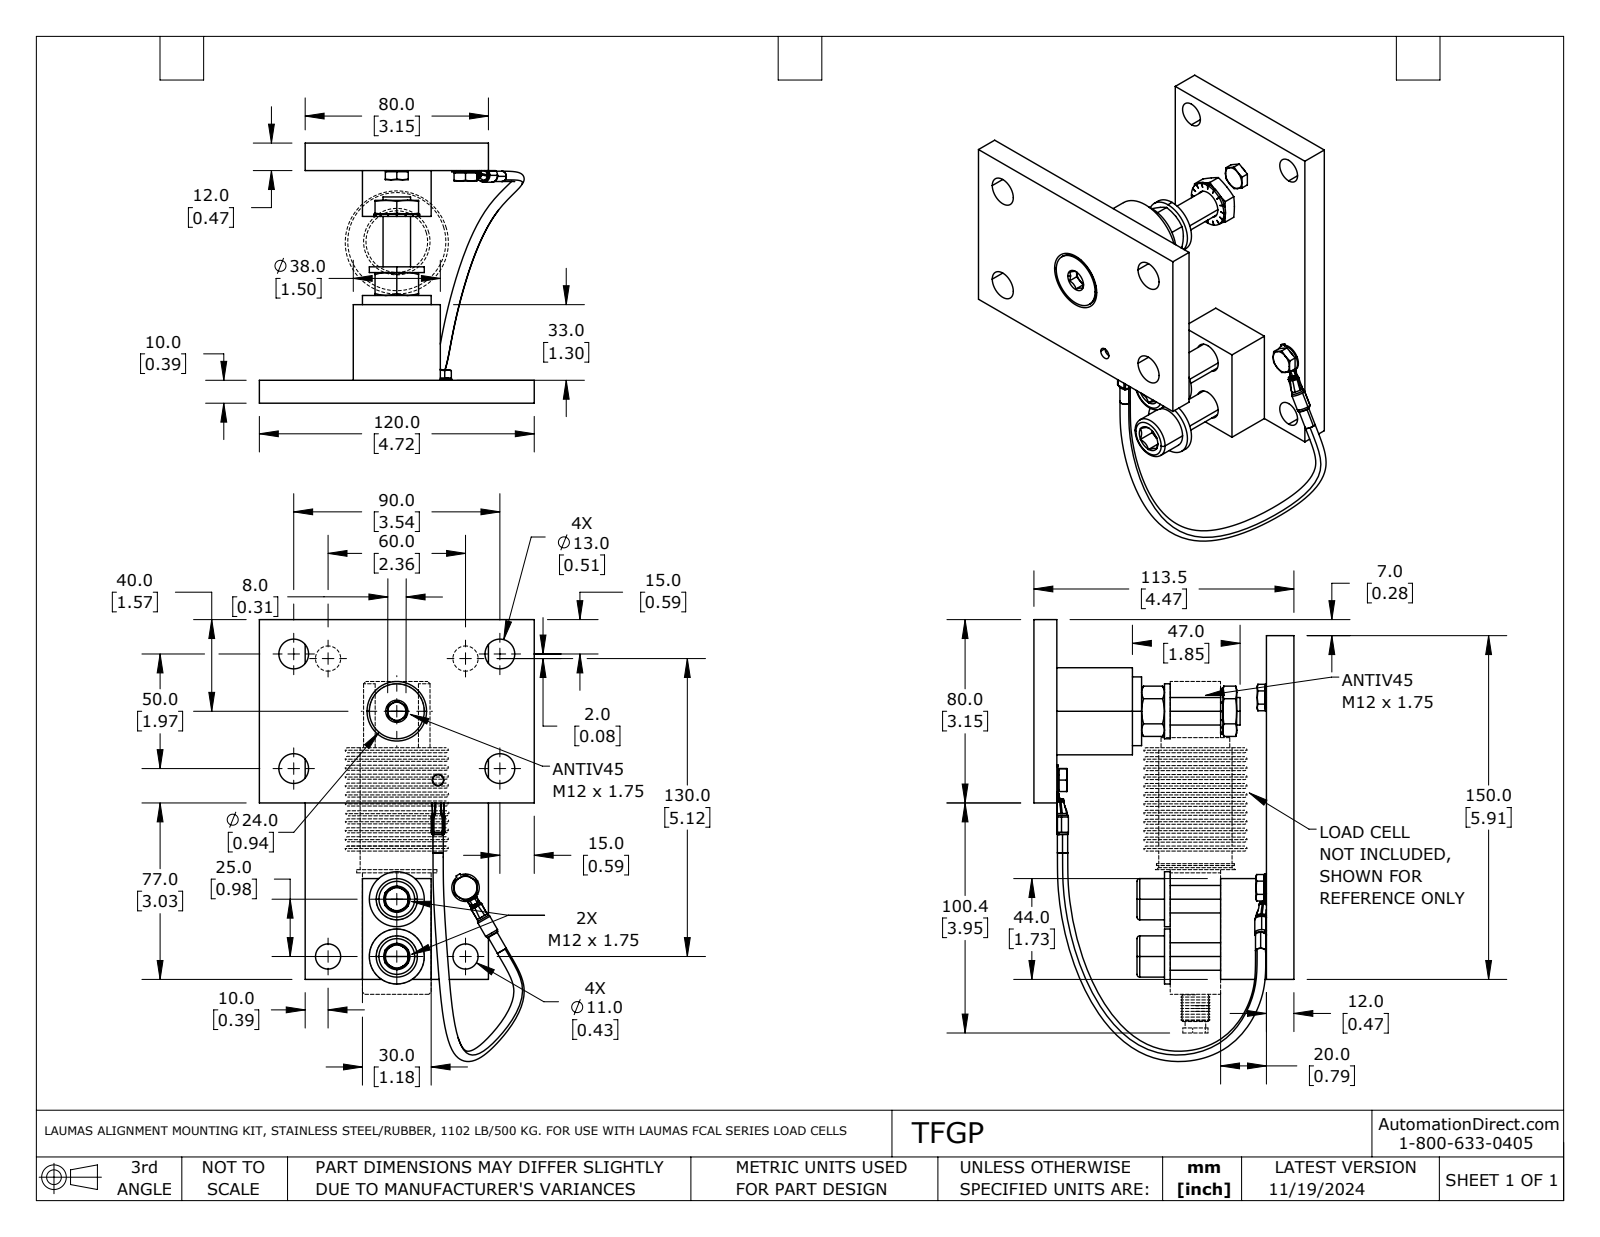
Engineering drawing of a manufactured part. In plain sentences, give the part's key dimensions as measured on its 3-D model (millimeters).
The part is named "TFGP". Its 3-D file was written by "SolidWorks 2021 (AUTOMOTIVE_DESIGN)". It is 24 solids with 639 faces: 230 planar, 190 cylindrical and 219 other. Overall it measures 192.8 by 120 by 113.5 millimeters. Its volume is 315 100 cubic millimeters and its surface area 103 400 square millimeters. Round holes: 7 of diameter 13, 4 of diameter 11, 3 of diameter 5, 3 of diameter 10.2, 2 of diameter 4, 2 of diameter 6, 1 of diameter 10.1, 1 of diameter 12.5, 1 of diameter 27, 1 of diameter 34. Round bosses or shafts: 5 of diameter 12, 3 of diameter 24, 3 of diameter 8.9, 2 of diameter 18, 2 of diameter 4.5, 1 of diameter 38, 1 of diameter 30, 1 of diameter 20. Partial cylindrical surfaces (rounded edges, fillets, slot ends): 8 of radius 0.5, 8 of radius 1.1, 8 of radius 1.3, 2 of radius 1, 2 of radius 3, 2 of radius 3, 2 of radius 3.5. The main face-to-face distances are 12, 10, 103.5, 91.5, 101.5, 113.5, 80, 20, 47, 45. The hole center spacings are 51.5, 111.1, 30, 15.1, 34.5, 37.8, 39, 48.8.
